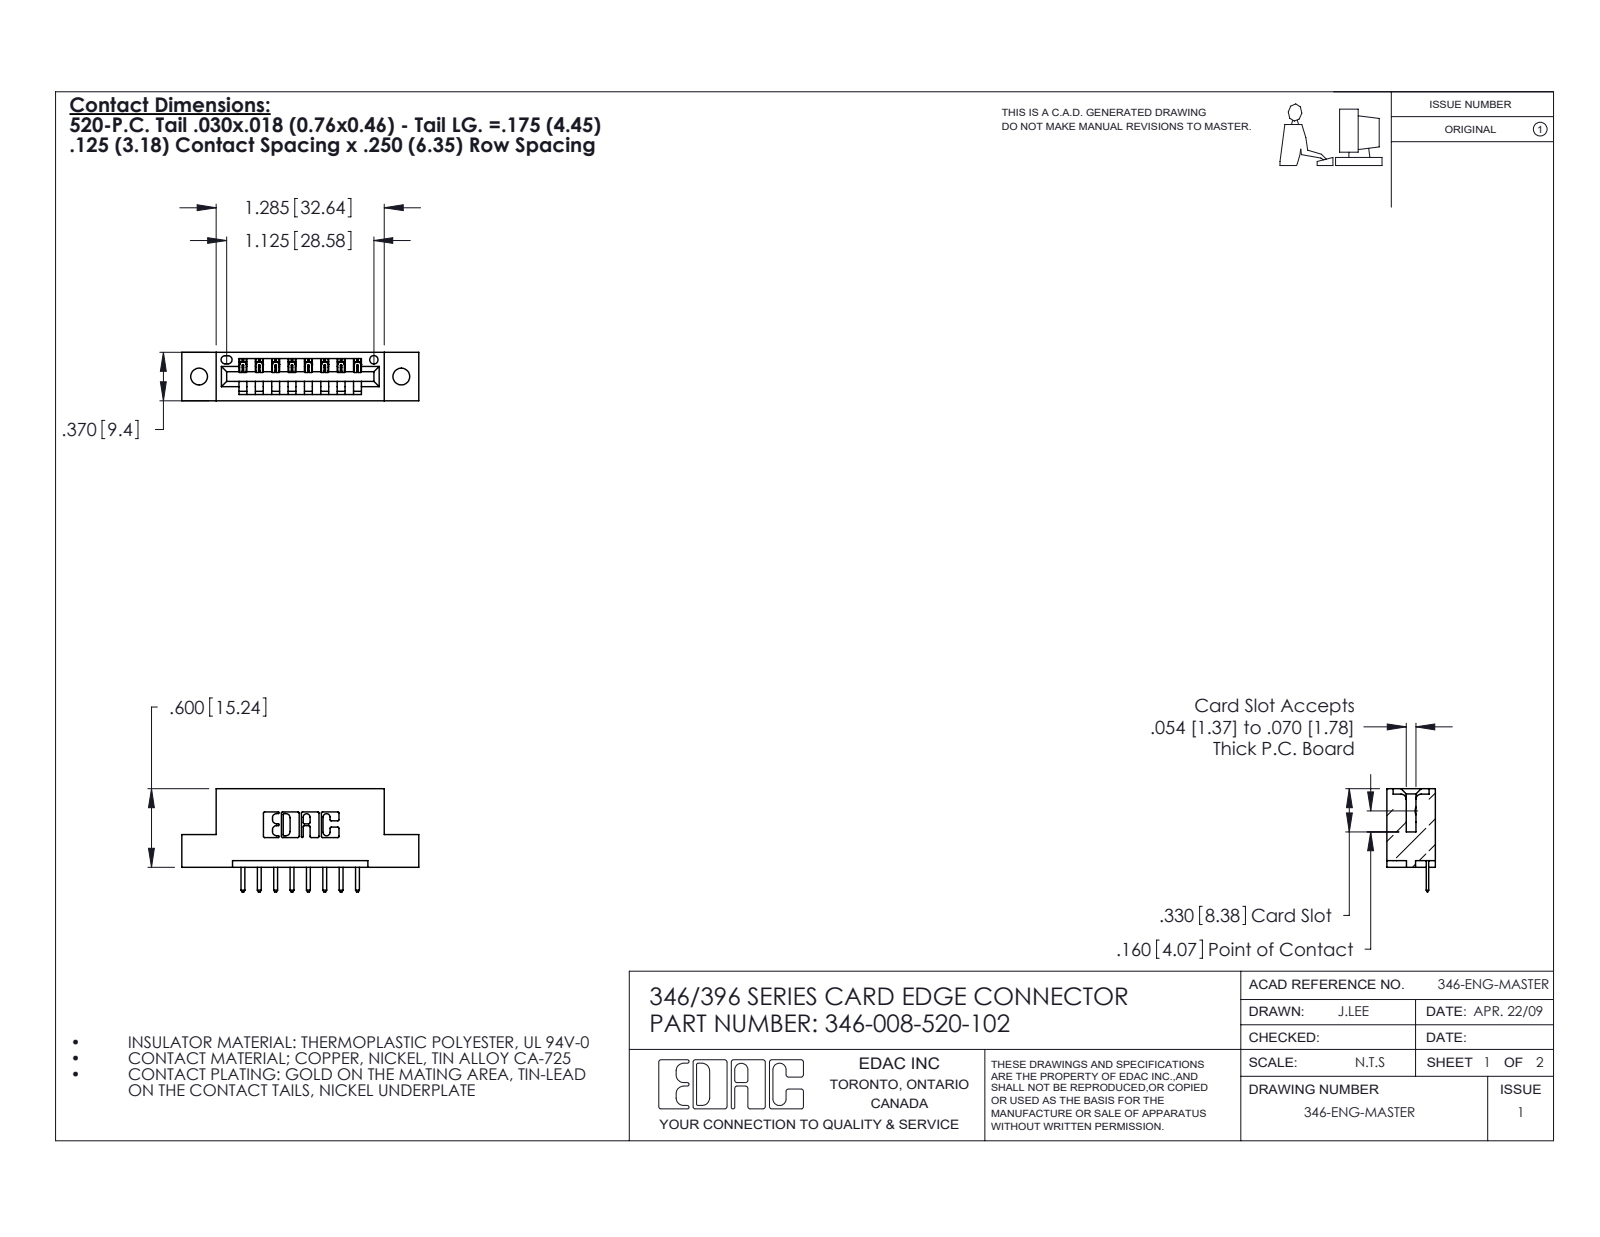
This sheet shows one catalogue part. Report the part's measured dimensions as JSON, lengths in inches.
{"part_name": "346 Part_Flush Mounting Lugs - 0.128 Dia; 346-008-520-102; 345-292-001_345-293-120", "step_written_by": "SolidWorks 2020 (CONFIG_CONTROL_DESIGN)", "units": "inches", "bodies": {"solids": 9, "faces": 618, "planar": 412, "cylindrical": 206, "other": 0}, "overall_size": [1.81, 0.788, 0.37], "volume_in3": 0.251, "surface_area_in2": 6.848, "round_holes": [[0.128, 2], [0.064, 1]], "partial_cylinders_radius": [[0.01, 22], [0.01, 18], [0.006, 16], [0.007, 6], [0.031, 6], [0.026, 3], [0.031, 2], [0.04, 2]], "face_to_face_distances": [0.25, 0.37, 0.048, 0.322, 0.5, 0.148, 0.222, 0.1, 0.174, 0.125], "hole_center_spacings": [0.246, 1.341, 1.545]}
